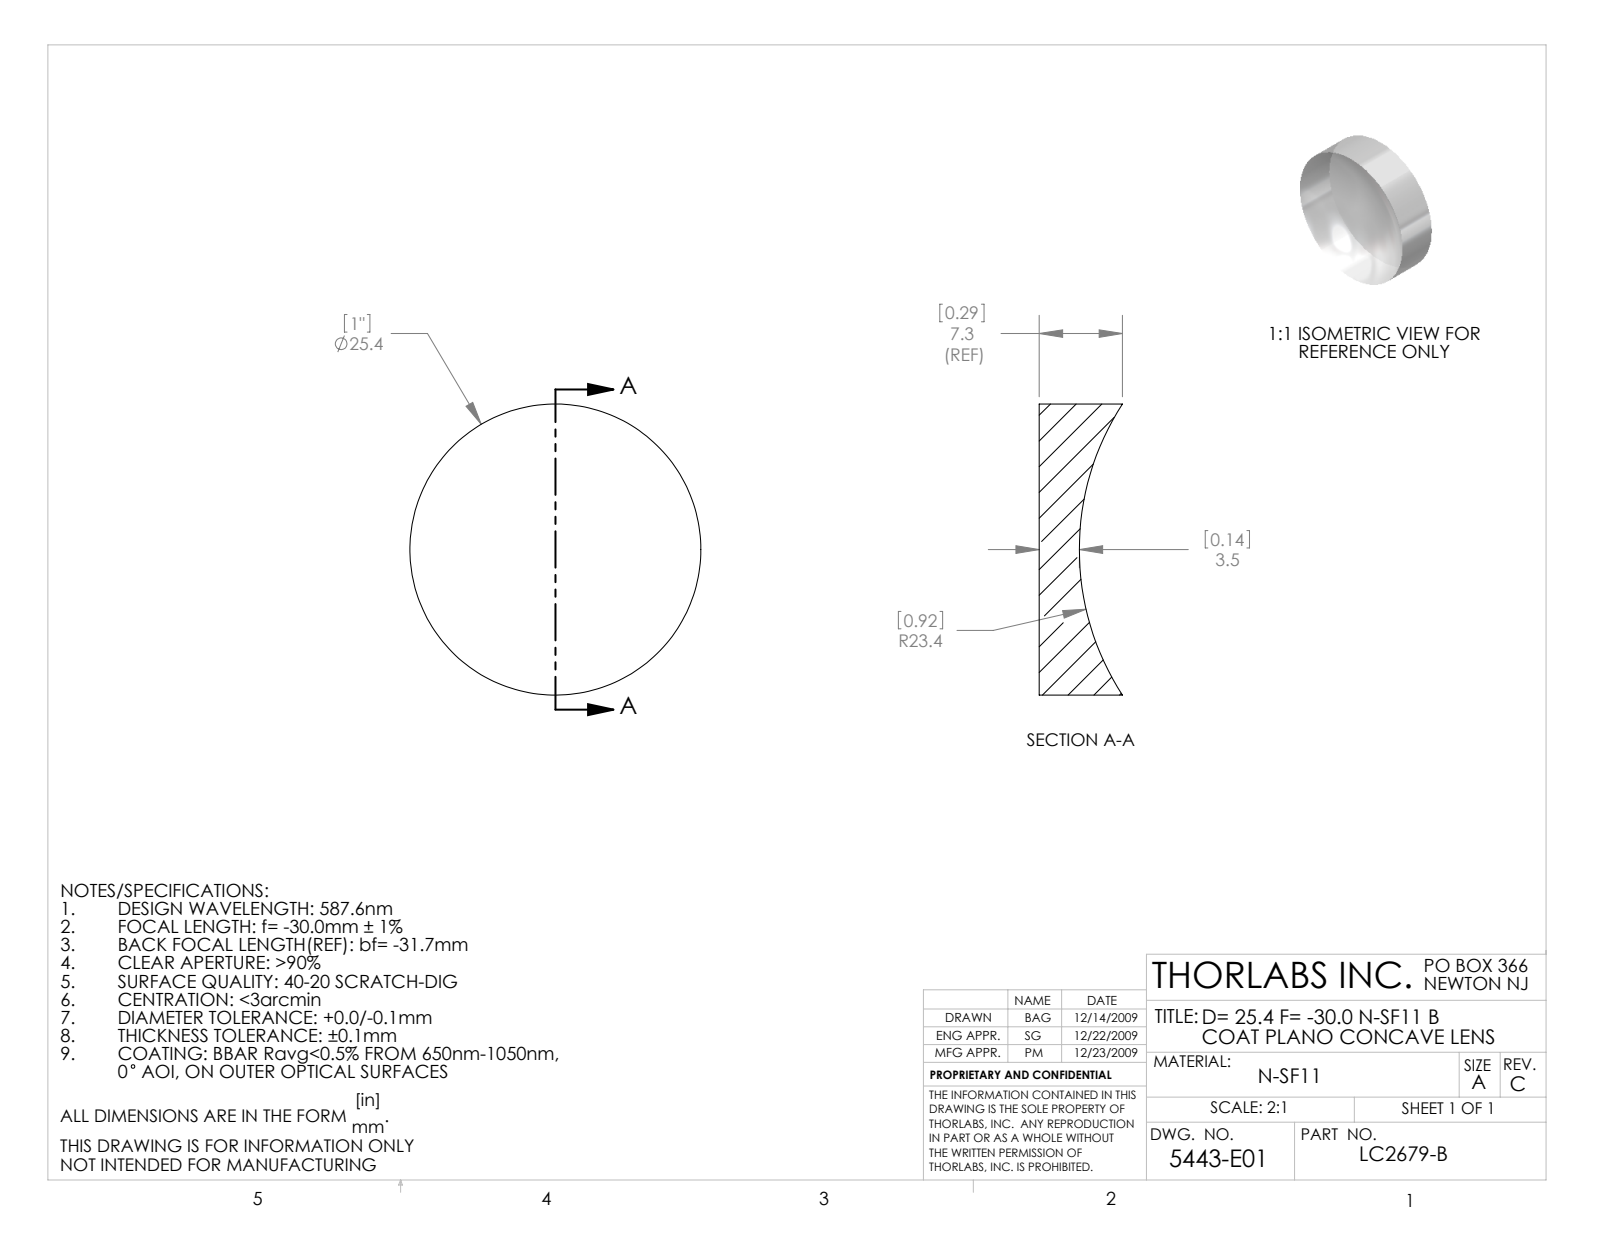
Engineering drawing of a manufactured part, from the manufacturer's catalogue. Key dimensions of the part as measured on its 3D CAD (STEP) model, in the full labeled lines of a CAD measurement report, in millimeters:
Part name (STEP PRODUCT): 5443-E0W
STEP written by: SolidWorks 2009 (AUTOMOTIVE_DESIGN)
Units: millimetres
Bodies: 1 solid, 5 faces (1 planar, 2 cylindrical, 2 other)
Overall size (bounding box): 25.4 × 25.4 × 7.3
Volume: 2 700 mm³ · Surface area: 1 637 mm²
Round bosses / shafts (diameter × count): ⌀25.4 ×1
